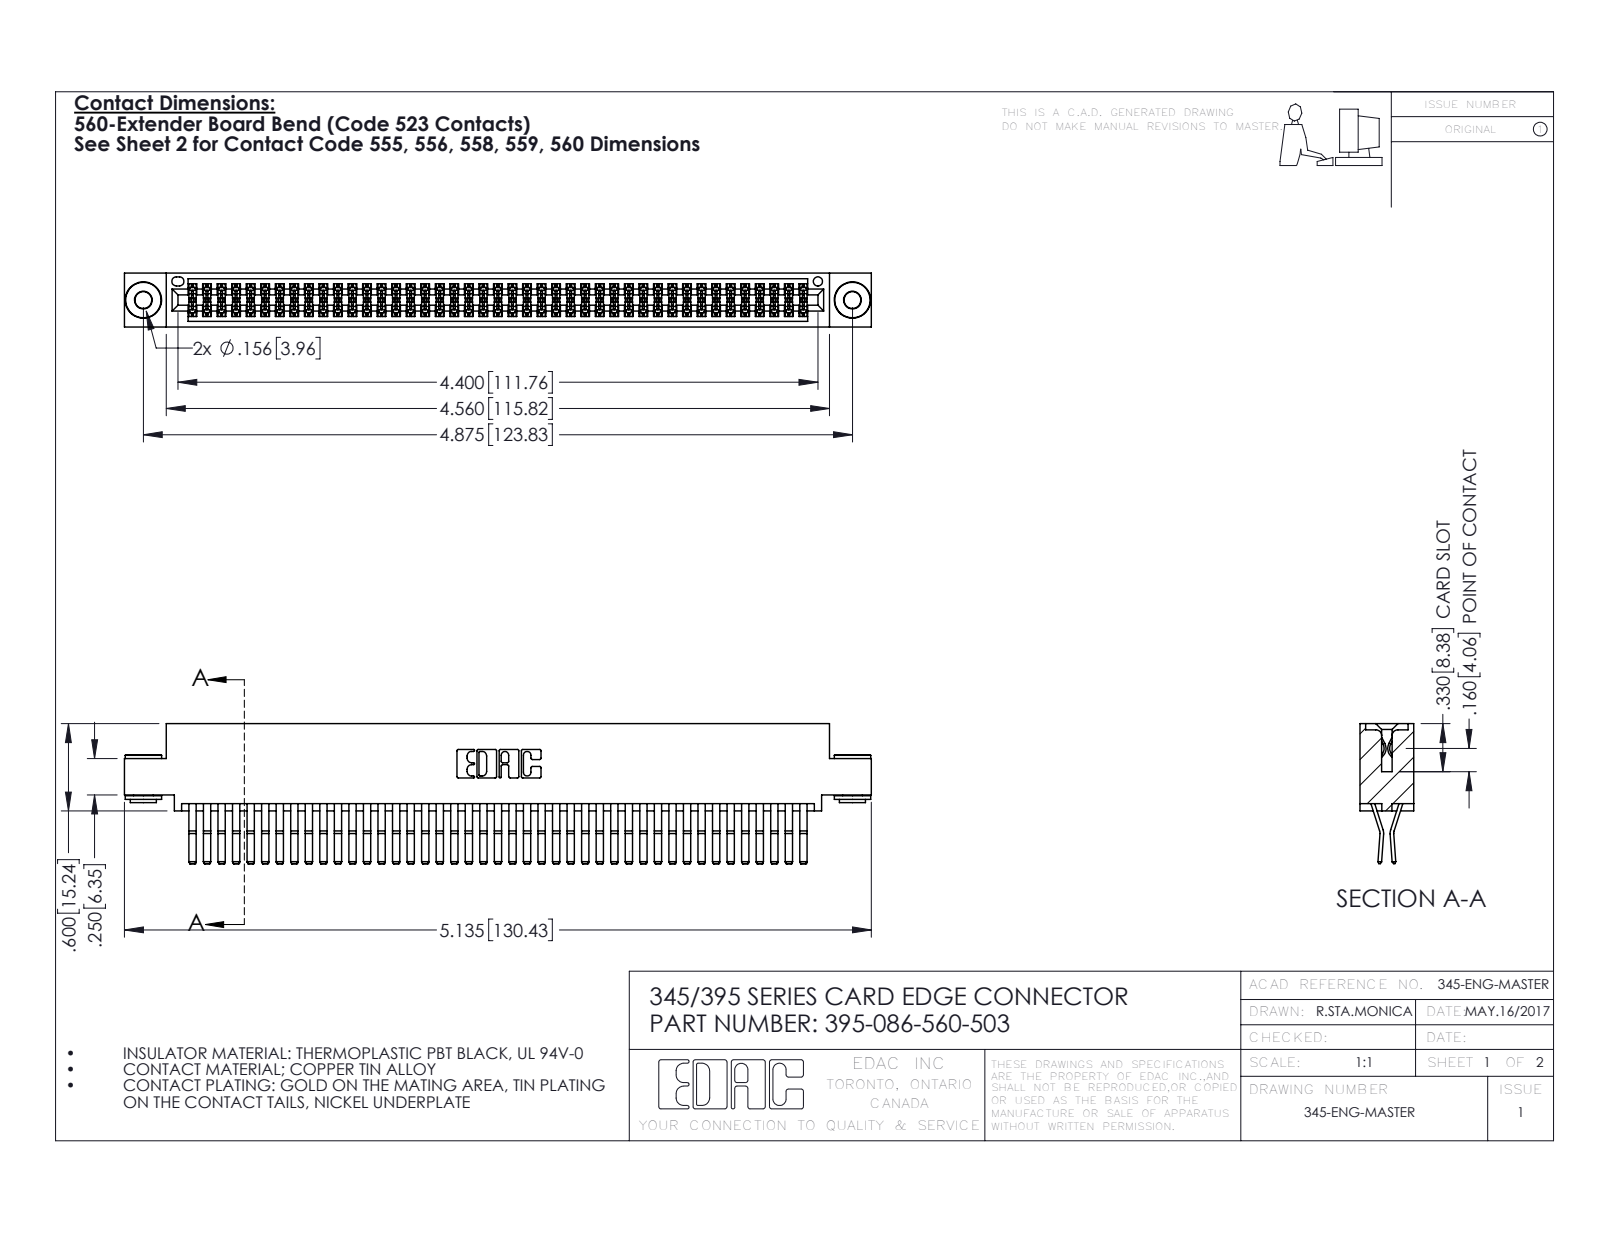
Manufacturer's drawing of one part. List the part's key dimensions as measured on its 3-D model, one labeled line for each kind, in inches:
Part name (STEP PRODUCT): 345-250-002_345-250-002-102; 345-292-001_560 Tail; 395-086-560-503; 345 Part_0.110 Offset - 0.156 Dia-TH
STEP written by: SolidWorks 2016 (CONFIG_CONTROL_DESIGN)
Units: inches
Bodies: 89 solids, 4640 faces (2932 planar, 1700 cylindrical, 8 other)
Overall size (bounding box): 5.135 × 0.962 × 0.37
Volume: 0.805 in³ · Surface area: 32.96 in²
Round holes (diameter × count): ⌀0.116 ×2, ⌀0.156 ×2, ⌀0.064 ×1
Round bosses / shafts (diameter × count): ⌀0.25 ×2, ⌀0.18 ×2, ⌀0.136 ×2
Partial cylindrical surfaces — rounded edges, fillets, slot ends (radius × count): R0.006 ×130, R0.01 ×22, R0.007 ×6, R0.031 ×6, R0.026 ×3, R0.01 ×2, R0.014 ×2, R0.019 ×2
Main face-to-face distances: 0.025, 0.072, 0.298, 0.37, 0.2, 0.098, 0.272, 0.225, 0.175, 0.149
Hole centre spacings: 0.27, 4.639, 4.875
